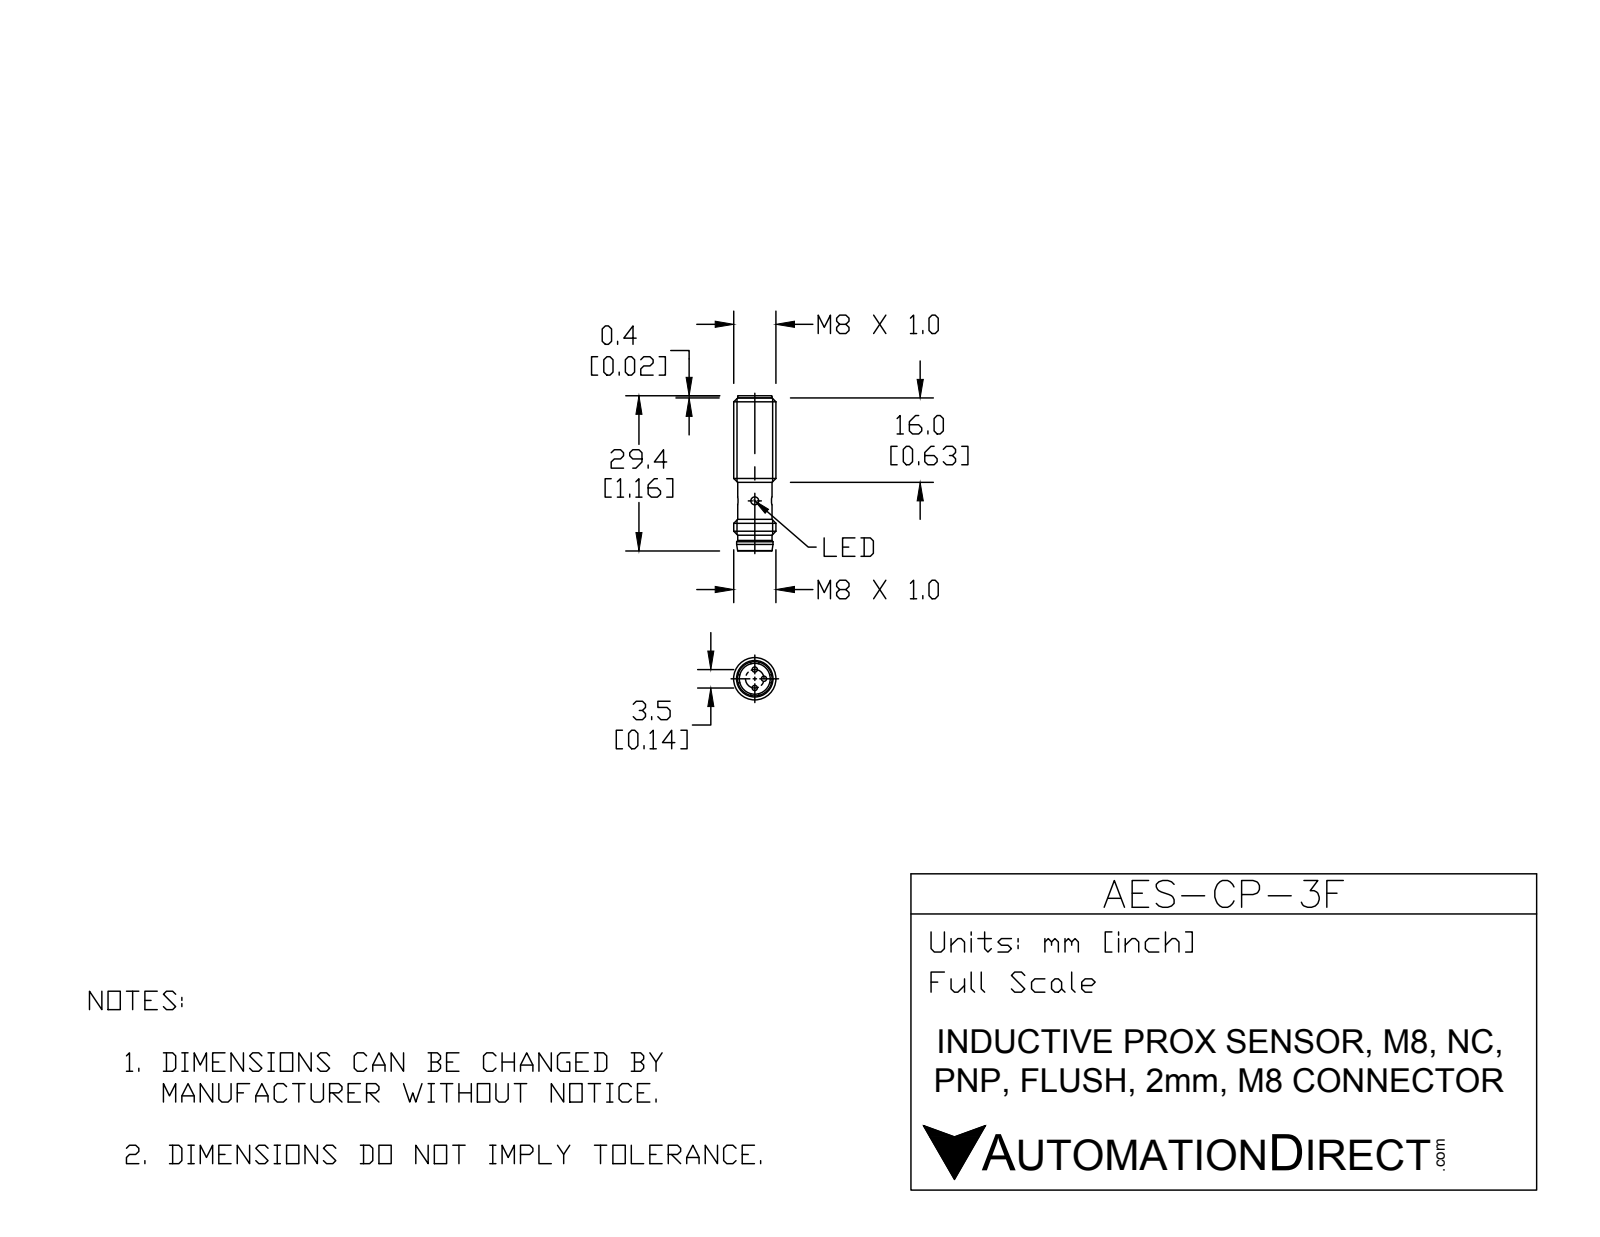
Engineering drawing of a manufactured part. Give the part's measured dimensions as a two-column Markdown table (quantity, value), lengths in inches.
| quantity | value |
| --- | --- |
| part name | AES-CP-3F |
| STEP written by | SolidWorks 2015 (CONFIG_CONTROL_DESIGN) |
| units | inches |
| bodies | 1 solid, 58 faces (10 planar, 28 cylindrical, 20 other) |
| overall size | 1.157 × 0.315 × 0.315 |
| volume | 0.071 in³ |
| surface area | 1.44 in² |
| round holes (diameter × count) | 0.059 × 2, 0.23 × 1 |
| round bosses / shafts (diameter × count) | 0.039 × 3, 0.315 × 1, 0.272 × 1, 0.256 × 1 |
| main face-to-face distances | 0.961, 0.118, 1.079, 0.217, 0.433, 0.315, 0.646, 1.063, 0.945, 0.63 |
